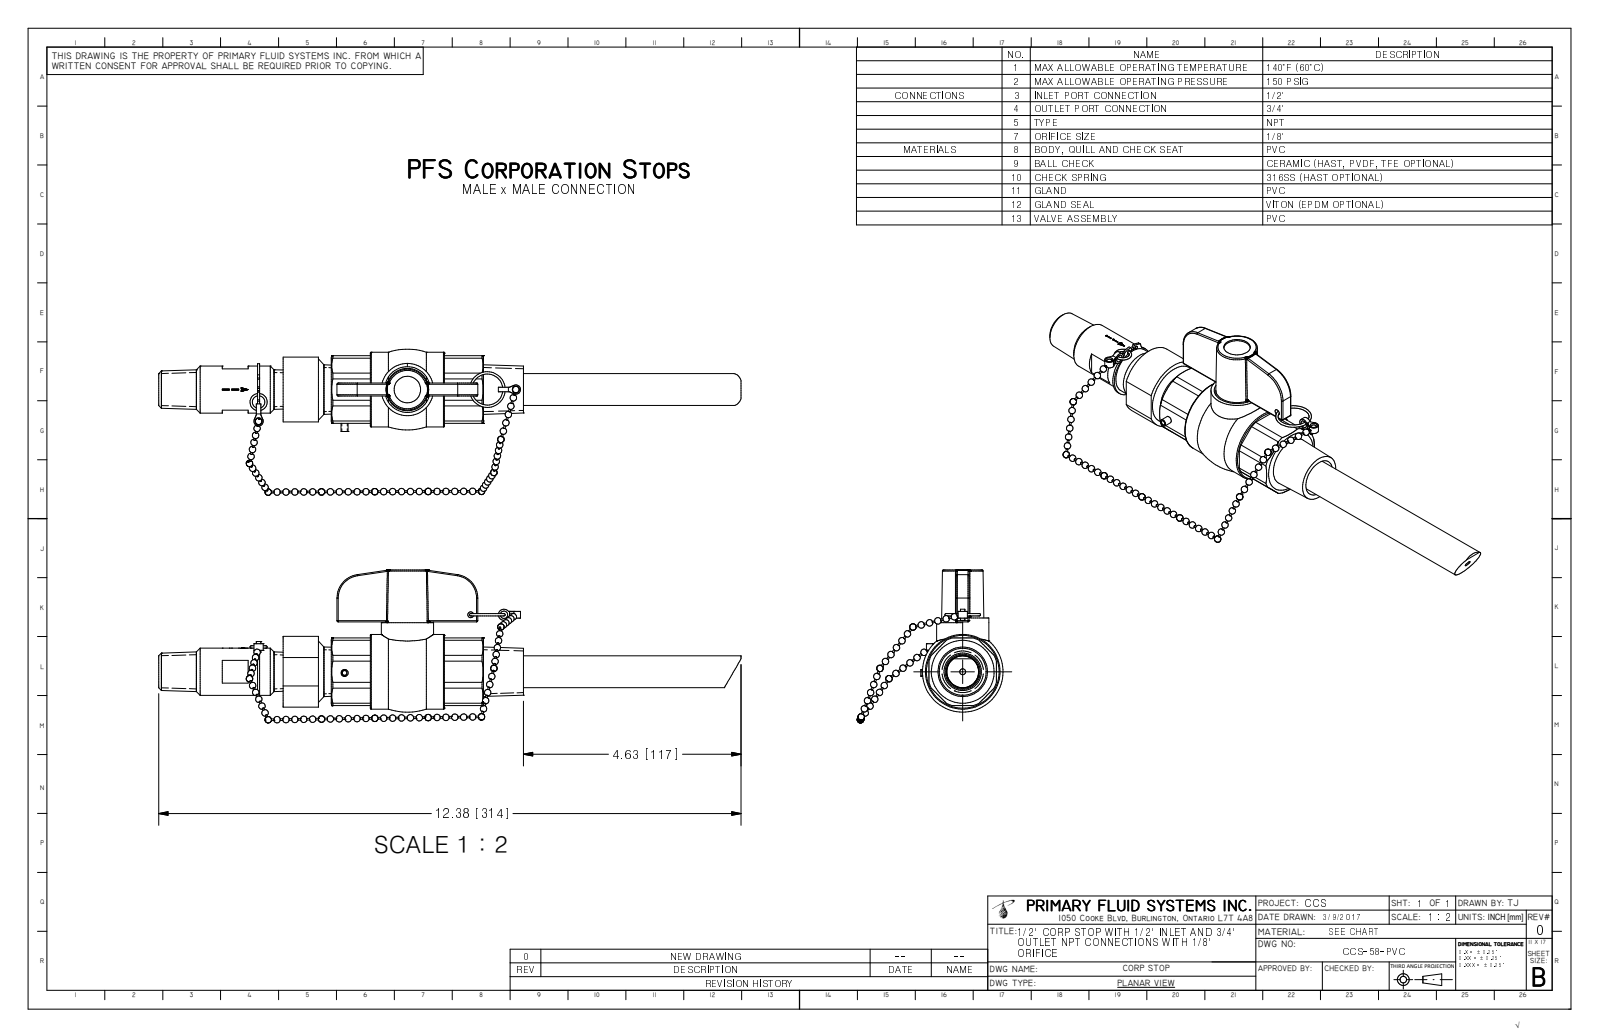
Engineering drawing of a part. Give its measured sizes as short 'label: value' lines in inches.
name: CCS-58-PVC_R0
written by: Autodesk Inventor 2009 (AUTOMOTIVE_DESIGN)
unit: in
bodies: 1 solid, 395 faces (115 planar, 60 cylindrical, 220 other)
size: 12.38 × 3.247 × 3.099
volume: 12.77 in³; area: 70.68 in²
holes: 1× ⌀0.079, 1× ⌀0.125, 1× ⌀0.15, 1× ⌀0.25, 1× ⌀0.469, 1× ⌀0.56, 1× ⌀0.563, 1× ⌀0.97
bosses: 1× ⌀1.585, 1× ⌀1.11, 1× ⌀1.094, 1× ⌀1, 1× ⌀0.9, 1× ⌀0.675, 1× ⌀0.558
rounds: 12× R0.025, 2× R0.043, 2× R0.157, 2× R0.5, 1× R0.451, 1× R0.463, 1× R0.499, 1× R0.614
face distances: 1.435, 0.03, 0.55, 0.275, 0.825, 0.58, 0.855, 1.405, 0.25, 1.024
hole spacings: 0.535
